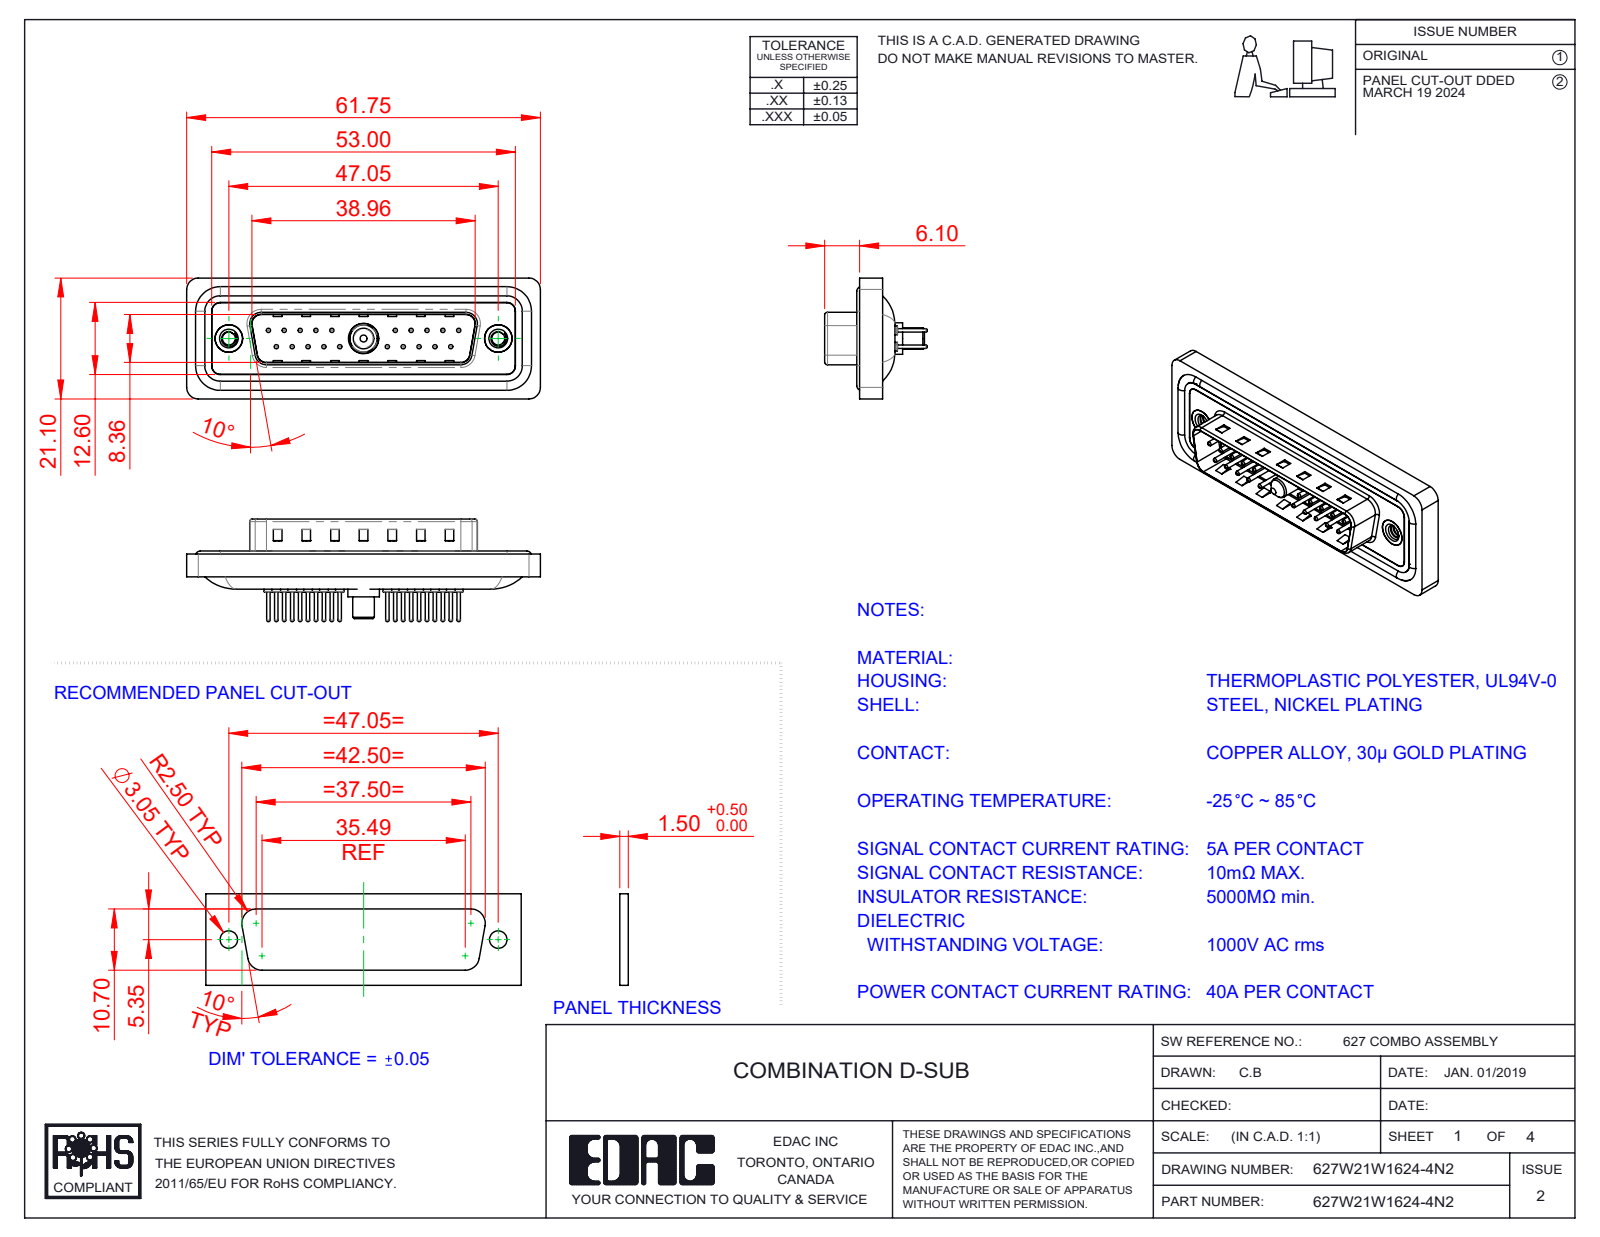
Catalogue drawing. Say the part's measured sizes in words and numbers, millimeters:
The part is named "627Combo Shell Rear_25 Contacts; 627Combo Waterproof Housing_25 Contacts; 627Combo Contact Row 2_24; 627Combo Housing_21W1 (+5 more)". Its 3-D file was written by "SolidWorks 2023 (CONFIG_CONTROL_DESIGN)". It is 29 solids with 1262 faces: 359 planar, 487 cylindrical and 416 other. Overall it measures 61.75 by 21.1 by 17.9 millimeters. Its volume is 7 216 cubic millimeters and its surface area 11 964 square millimeters. Round holes: 20 of diameter 0.75, 20 of diameter 1.6, 20 of diameter 2, 2 of diameter 2.26, 2 of diameter 4, 2 of diameter 4.8, 2 of diameter 5, 1 of diameter 4.85, 1 of diameter 5.3. Round bosses or shafts: 20 of diameter 1.5, 20 of diameter 0.6, 4 of diameter 1.6, 2 of diameter 4.9, 1 of diameter 5.5, 1 of diameter 5.2, 1 of diameter 4.75, 1 of diameter 3.75. Partial cylindrical surfaces (rounded edges, fillets, slot ends): 22 of radius 1.5, 18 of radius 2, 8 of radius 0.5, 8 of radius 1.6, 4 of radius 0.25, 4 of radius 0.6, 4 of radius 0.65, 4 of radius 0.9. The main face-to-face distances are 0.4, 1.5, 1.1, 1.6, 0.5, 3.1, 2.9, 4.1, 0.82, 9.58. The hole center spacings are 3.16, 2.77, 5.54, 8.31, 5.04, 19.39, 20.97, 22.16.
